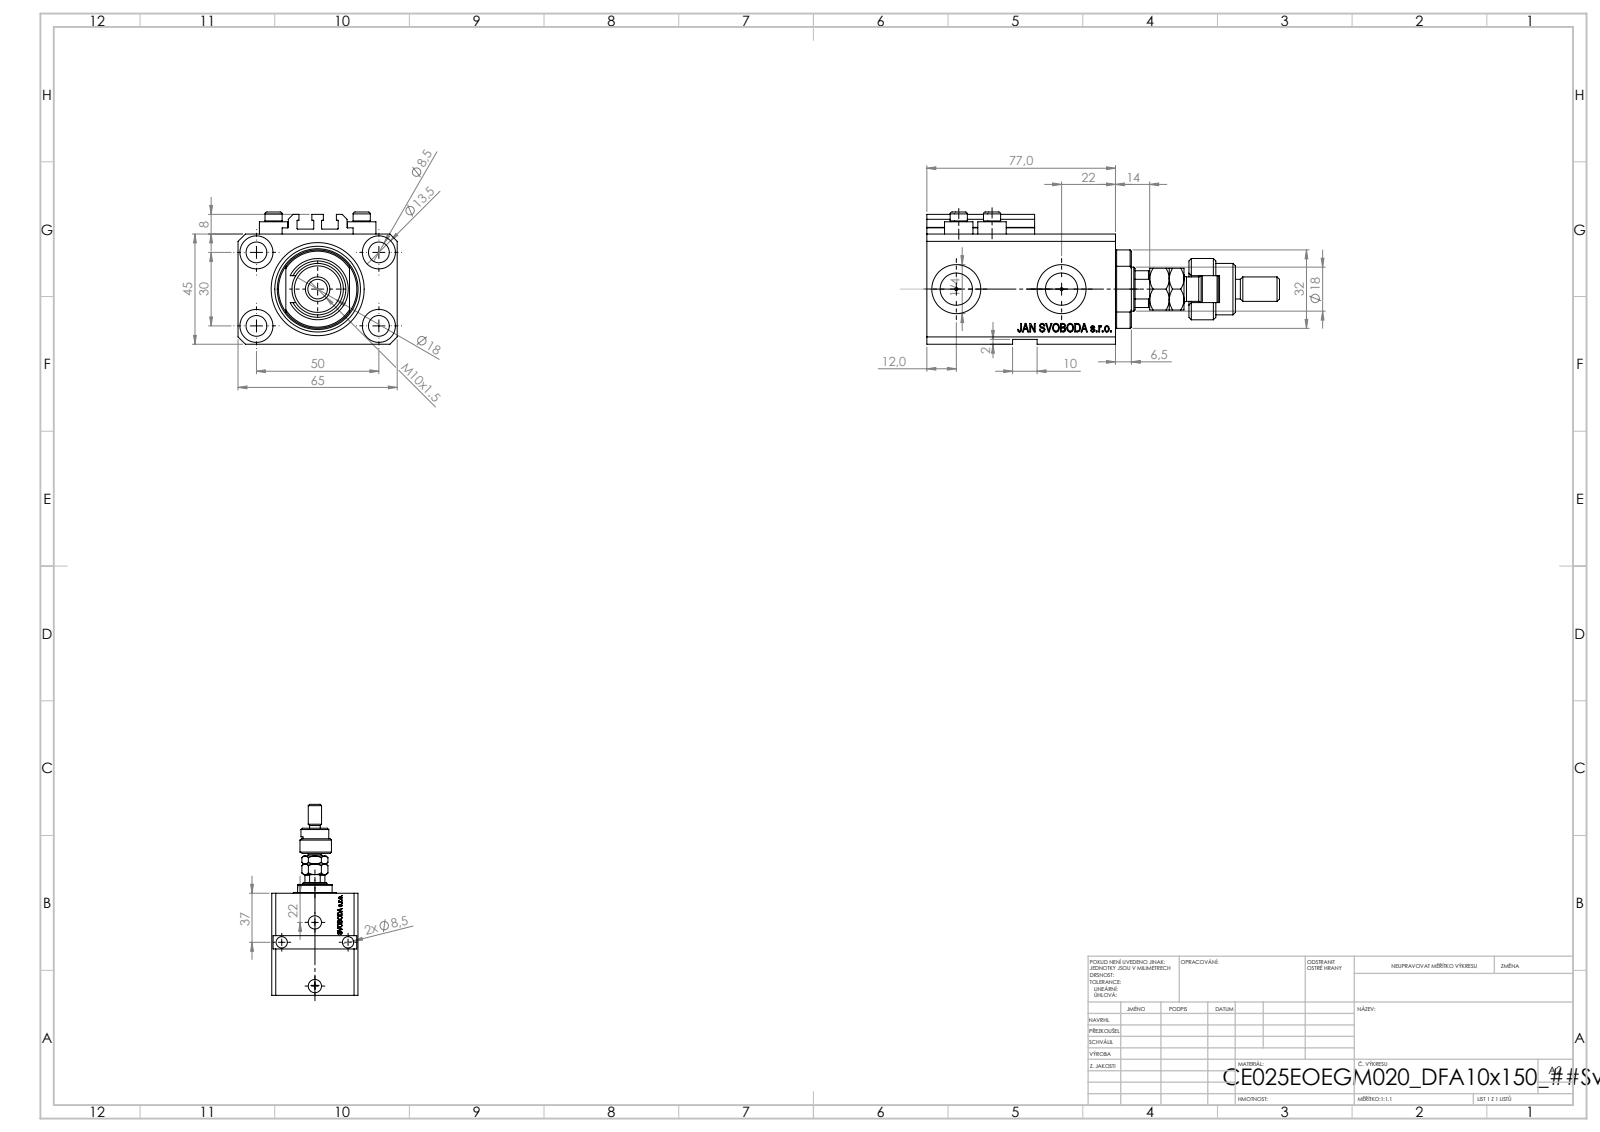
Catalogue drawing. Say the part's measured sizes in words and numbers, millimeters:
The part is named "V250CE_C_VCP; FEMALE_PART_FOR_DFA; ALLEN BOLT V250CE; MFA (+2 more)". Its 3-D file was written by "SolidWorks 2019 (CONFIG_CONTROL_DESIGN)". It is 10 solids with 1152 faces: 539 planar, 139 cylindrical and 474 other. Overall it measures 144 by 65 by 54 millimeters. Its volume is 211 569 cubic millimeters and its surface area 64 631 square millimeters. Round holes: 7 of diameter 8.5, 4 of diameter 1.25, 4 of diameter 4, 4 of diameter 13.5, 2 of diameter 10, 2 of diameter 13.16, 2 of diameter 20, 1 of diameter 18, 1 of diameter 38. Round bosses or shafts: 4 of diameter 11.6, 4 of diameter 7, 1 of diameter 25, 1 of diameter 21, 1 of diameter 16, 1 of diameter 10, 1 of diameter 8. Partial cylindrical surfaces (rounded edges, fillets, slot ends): 10 of radius 0.2, 1 of radius 5.5, 1 of radius 8.5, 1 of radius 8.75, 1 of radius 16. The main face-to-face distances are 45, 14, 65, 63, 77, 2, 3, 5, 6.9, 56.1. The hole center spacings are 29.15, 50, 13.6, 15.12, 18.81, 18.97, 26.22, 26.61.
